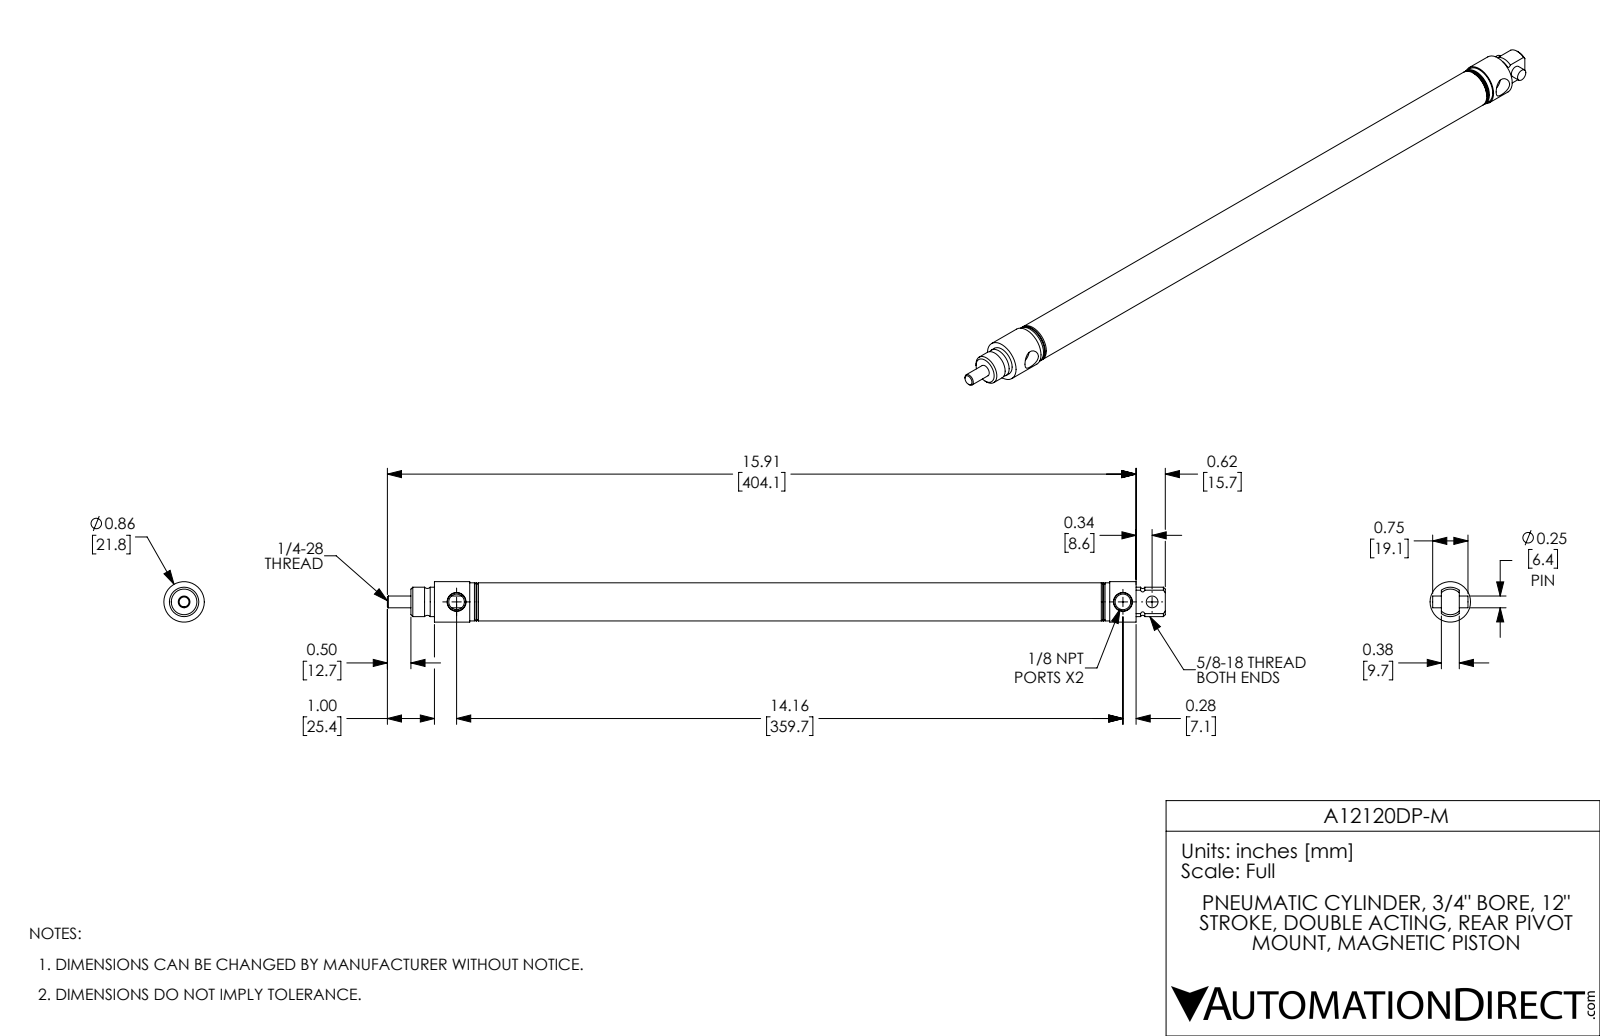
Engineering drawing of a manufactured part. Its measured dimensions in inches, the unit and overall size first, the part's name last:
Units: inches
Overall size (bounding box): 16.53 × 0.86 × 0.86
Round holes (diameter × count): ⌀0.25 ×2, ⌀0.332 ×2, ⌀0.75 ×1
Round bosses / shafts (diameter × count): ⌀0.86 ×1, ⌀0.81 ×1, ⌀0.625 ×1
Main face-to-face distances: 0.5, 13.705, 12.5, 12, 1.205, 1.705, 13.705, 14.91, 13.205, 1.205
Hole centre spacings: 0.62, 14.16, 14.78
Volume: 3.287 in³ · Surface area: 88.33 in²
Bodies: 3 solids, 91 faces (21 planar, 38 cylindrical, 32 other)
Part name (STEP PRODUCT): A12120DP-M-Rod; A12120DP-M-MainBody; A12120DP-M-PIN; A12120DP-M
STEP written by: SolidWorks 2017 (AUTOMOTIVE_DESIGN)
